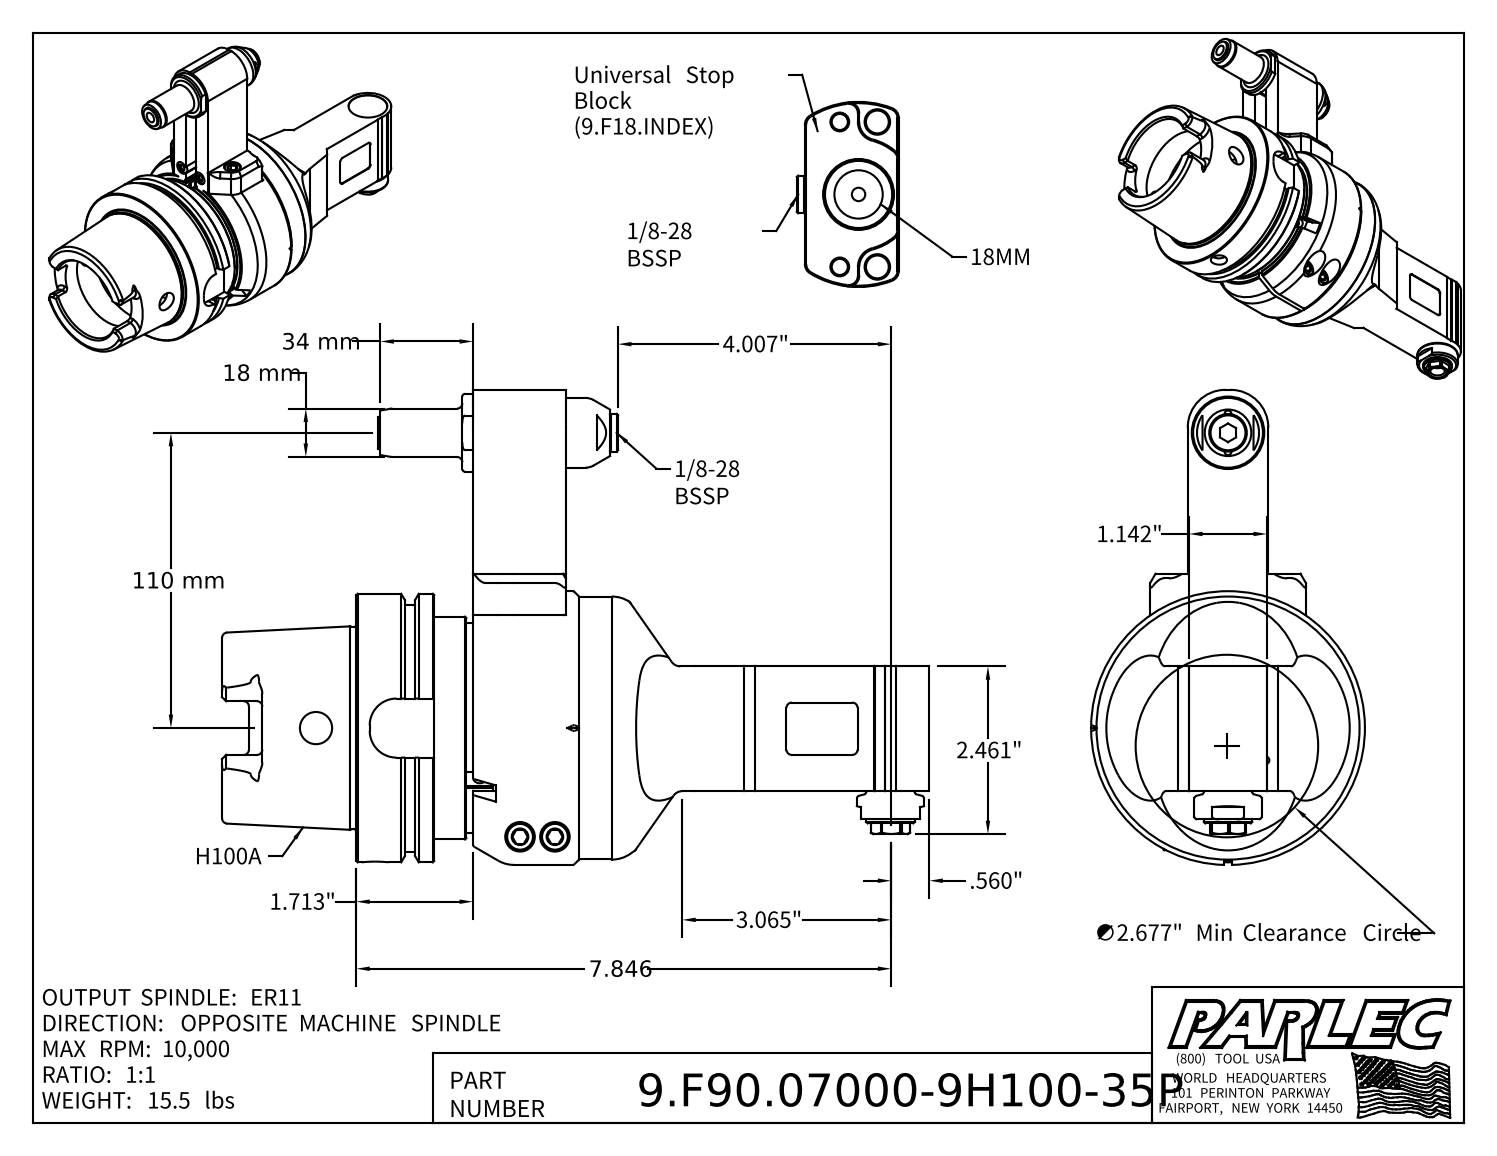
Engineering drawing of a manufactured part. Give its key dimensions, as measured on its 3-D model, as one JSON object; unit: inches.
{"part_name": "F900700-0000001L_511", "step_written_by": "CREO PARAMETRIC BY PTC INC, 2022244 (CONFIG_CONTROL_DESIGN)", "units": "inches", "bodies": {"solids": 1, "faces": 724, "planar": 270, "cylindrical": 251, "other": 203}, "overall_size": [10.374, 6.968, 4.016], "volume_in3": 65.54, "surface_area_in2": 219, "round_holes": [[0.197, 3], [0.256, 3], [0.102, 2], [0.13, 2], [0.165, 2], [0.315, 2], [0.335, 2], [0.409, 2], [0.433, 2], [0.492, 2], [1.063, 2], [0.098, 1]], "round_bosses_or_shafts": [[0.394, 4], [0.709, 3], [0.472, 2], [0.315, 2], [0.236, 2], [0.098, 2], [4.016, 1], [3.937, 1]], "partial_cylinders_radius": [[0.079, 18], [0.039, 14], [0.118, 6], [0.157, 5], [0.192, 4], [0.394, 4], [0.02, 2], [0.315, 2]], "face_to_face_distances": [1.142, 1.161, 0.02, 0.65, 1.555, 1.713, 0.335, 0.768, 1.831, 0.394], "hole_center_spacings": [0.276, 0.618, 1.994, 2.11, 2.383, 2.657, 3.498, 0.014]}
